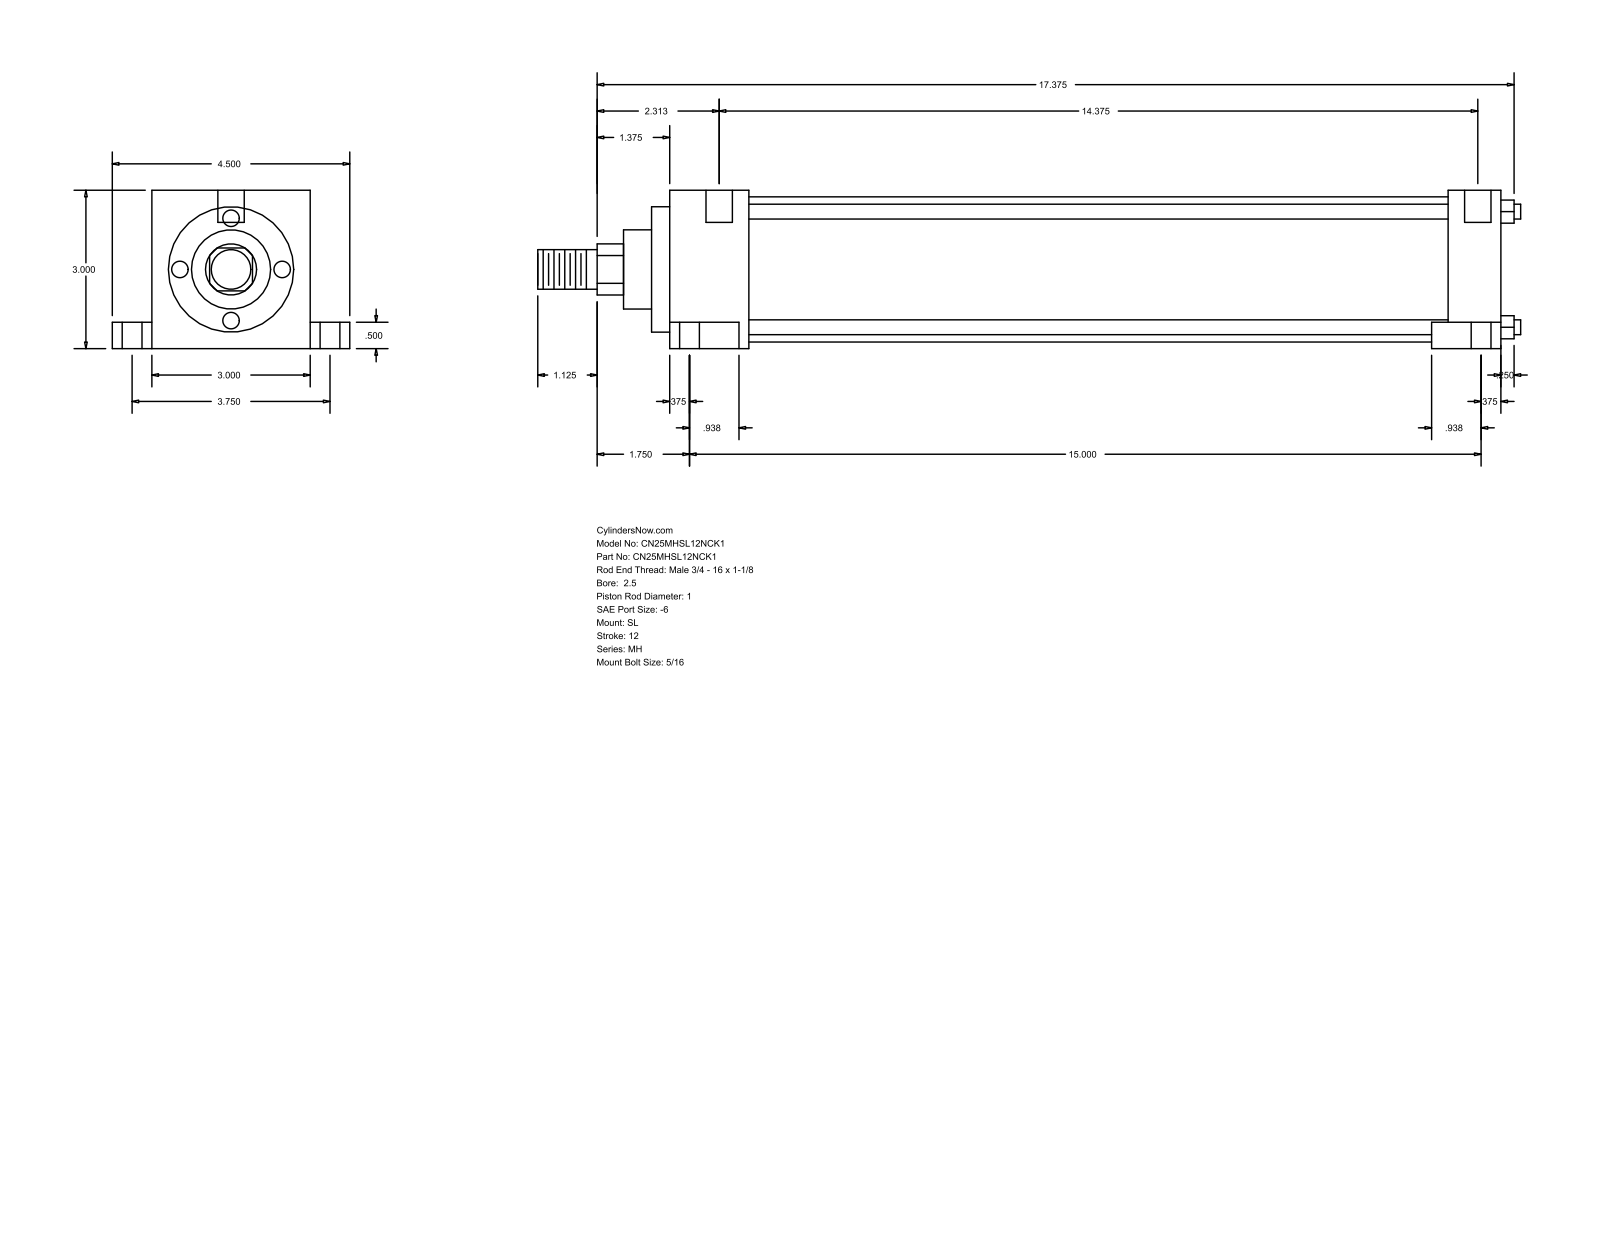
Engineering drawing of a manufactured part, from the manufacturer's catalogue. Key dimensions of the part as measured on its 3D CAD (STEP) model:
Part name (STEP PRODUCT): MH_SL__0250_1
STEP written by: GSSL Pune (CONFIG_CONTROL_DESIGN)
Units: millimetres
Bodies: 0 solids, 86 faces (61 planar, 25 cylindrical, 0 other)
Overall size (bounding box): 473.07 × 114.3 × 76.2
Round holes (diameter × count): ⌀5.56 ×2, ⌀9.53 ×2, ⌀15.88 ×2, ⌀12.7 ×1
Round bosses / shafts (diameter × count): ⌀7.14 ×4, ⌀69.85 ×1, ⌀60.33 ×1, ⌀38.1 ×1, ⌀25.4 ×1, ⌀19.05 ×1
Partial cylindrical surfaces — rounded edges, fillets, slot ends (radius × count): R12.29 ×1
Main face-to-face distances: 76.2, 25.41, 383.38, 408.79, 12.7, 63.5, 19.05, 95.25, 13.49, 396.87
Hole centre spacings: 47.65, 3.18, 95.24
